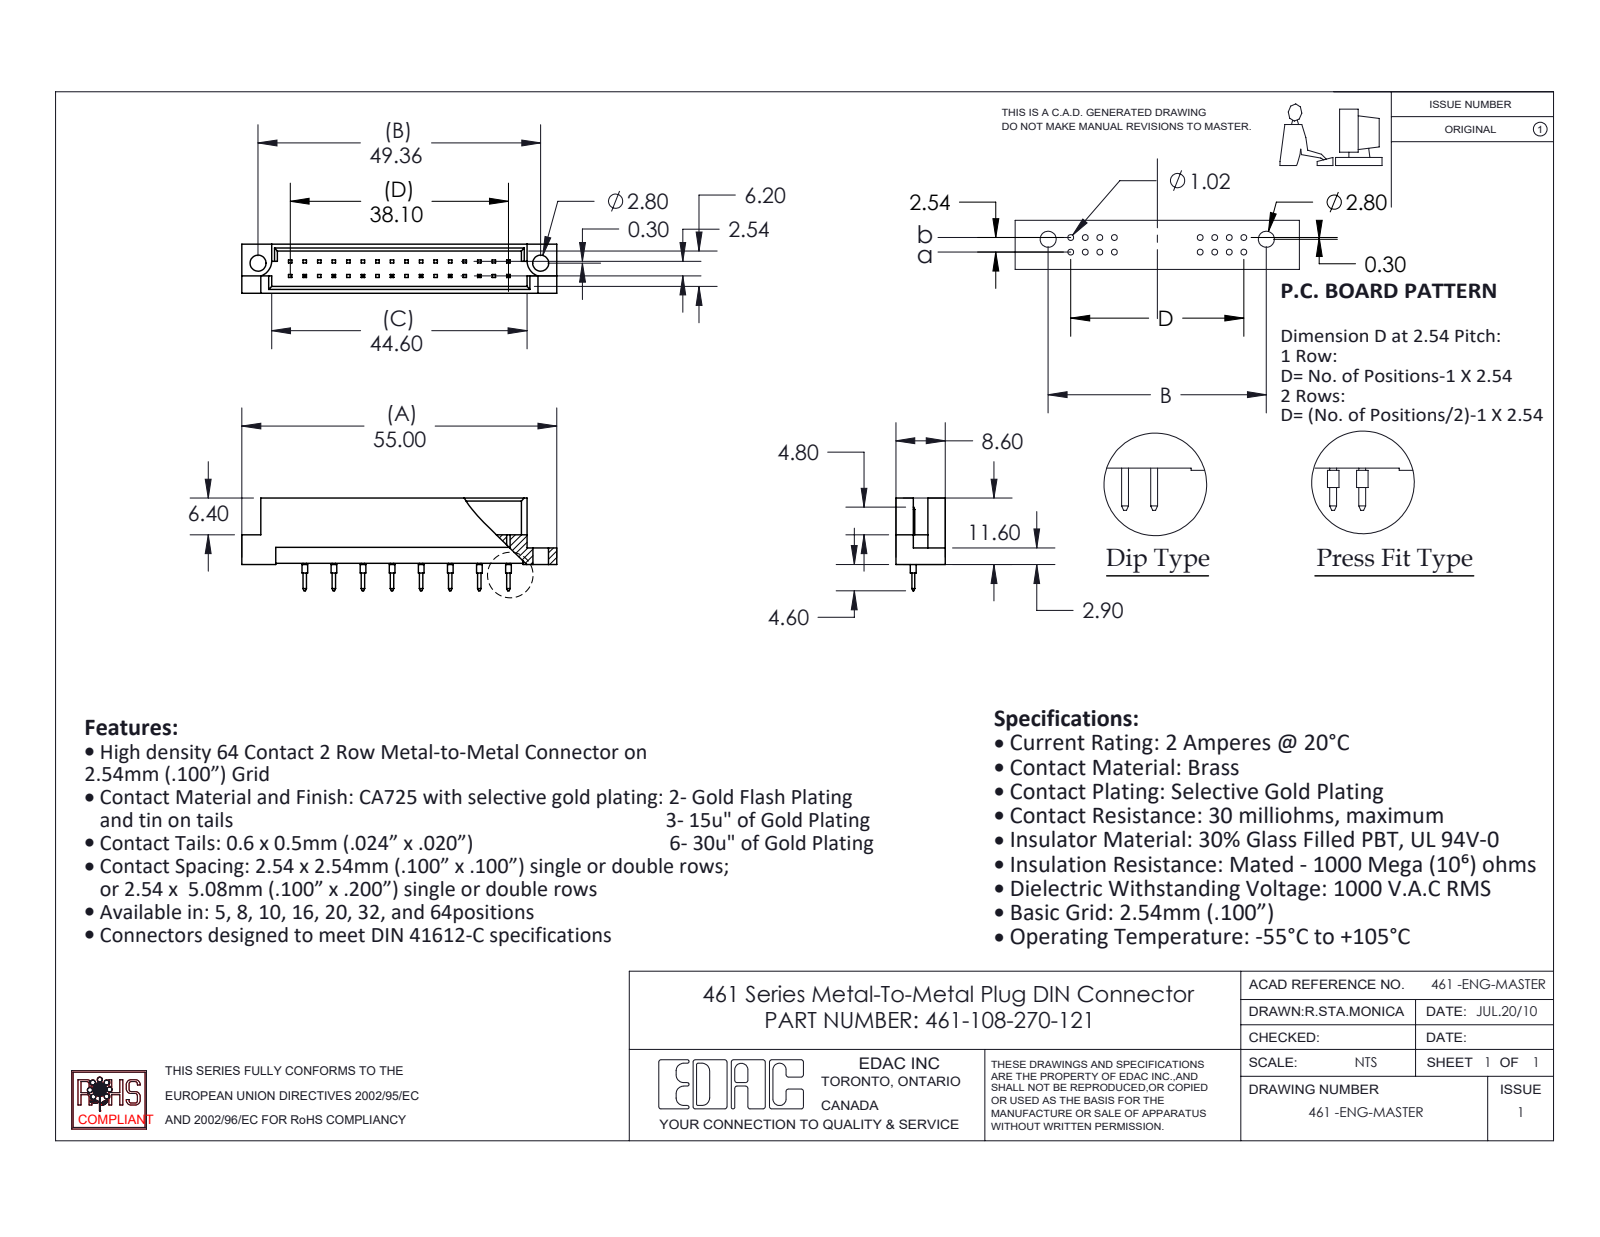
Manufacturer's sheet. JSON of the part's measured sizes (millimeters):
{"part_name": "461-108-270-121; 461-290_70; 461 Part_32", "step_written_by": "SolidWorks 2020 (CONFIG_CONTROL_DESIGN)", "units": "millimeters", "bodies": {"solids": 9, "faces": 352, "planar": 330, "cylindrical": 22, "other": 0}, "overall_size": [55, 16.2, 8.6], "volume_mm3": 2694, "surface_area_mm2": 3521, "round_holes": [[2.8, 2]], "round_bosses_or_shafts": [[1, 8]], "partial_cylinders_radius": [[2.8, 2]], "face_to_face_distances": [1.2, 7.4, 8.6, 6.2, 5, 5.2, 1.58, 2.78, 5.82, 4.62], "hole_center_spacings": [49.36]}
